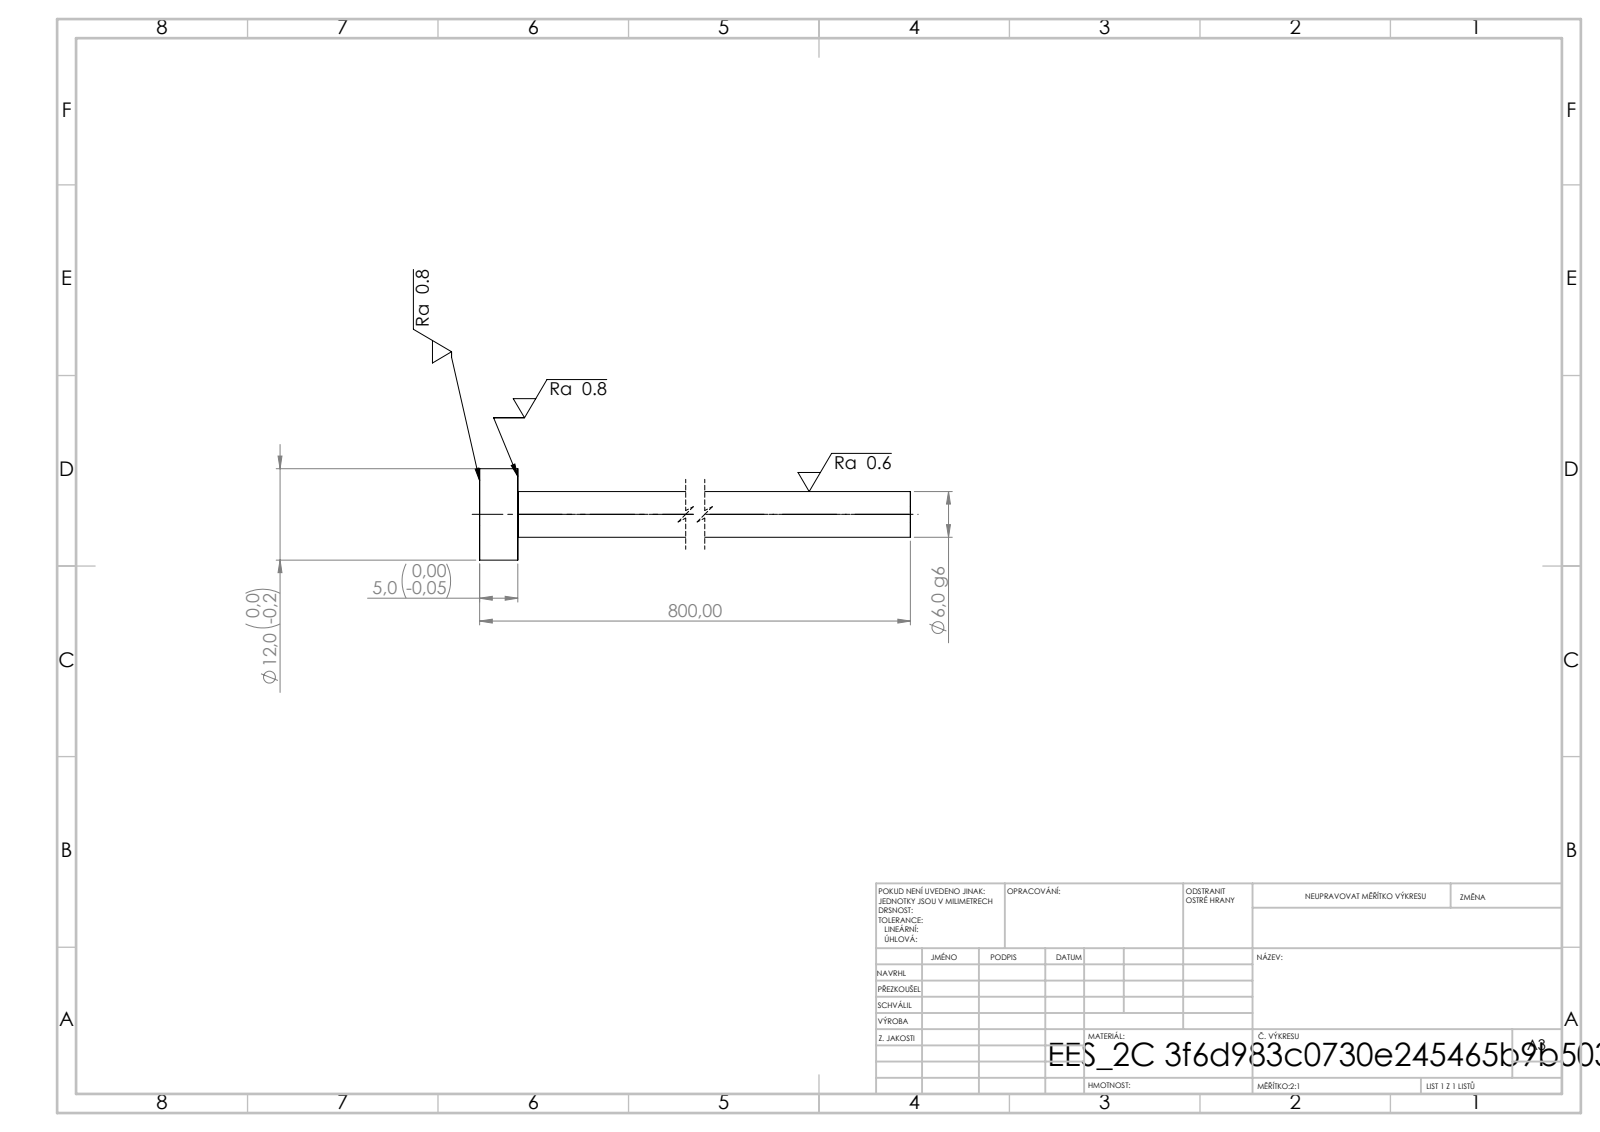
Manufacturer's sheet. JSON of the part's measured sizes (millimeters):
{"step_written_by": "SolidWorks 2019 (CONFIG_CONTROL_DESIGN)", "units": "millimeters", "bodies": {"solids": 1, "faces": 7, "planar": 3, "cylindrical": 4, "other": 0}, "overall_size": [800, 12, 12], "volume_mm3": 23044, "surface_area_mm2": 15400, "round_bosses_or_shafts": [[12, 1], [6, 1]], "face_to_face_distances": [5, 800, 795]}
